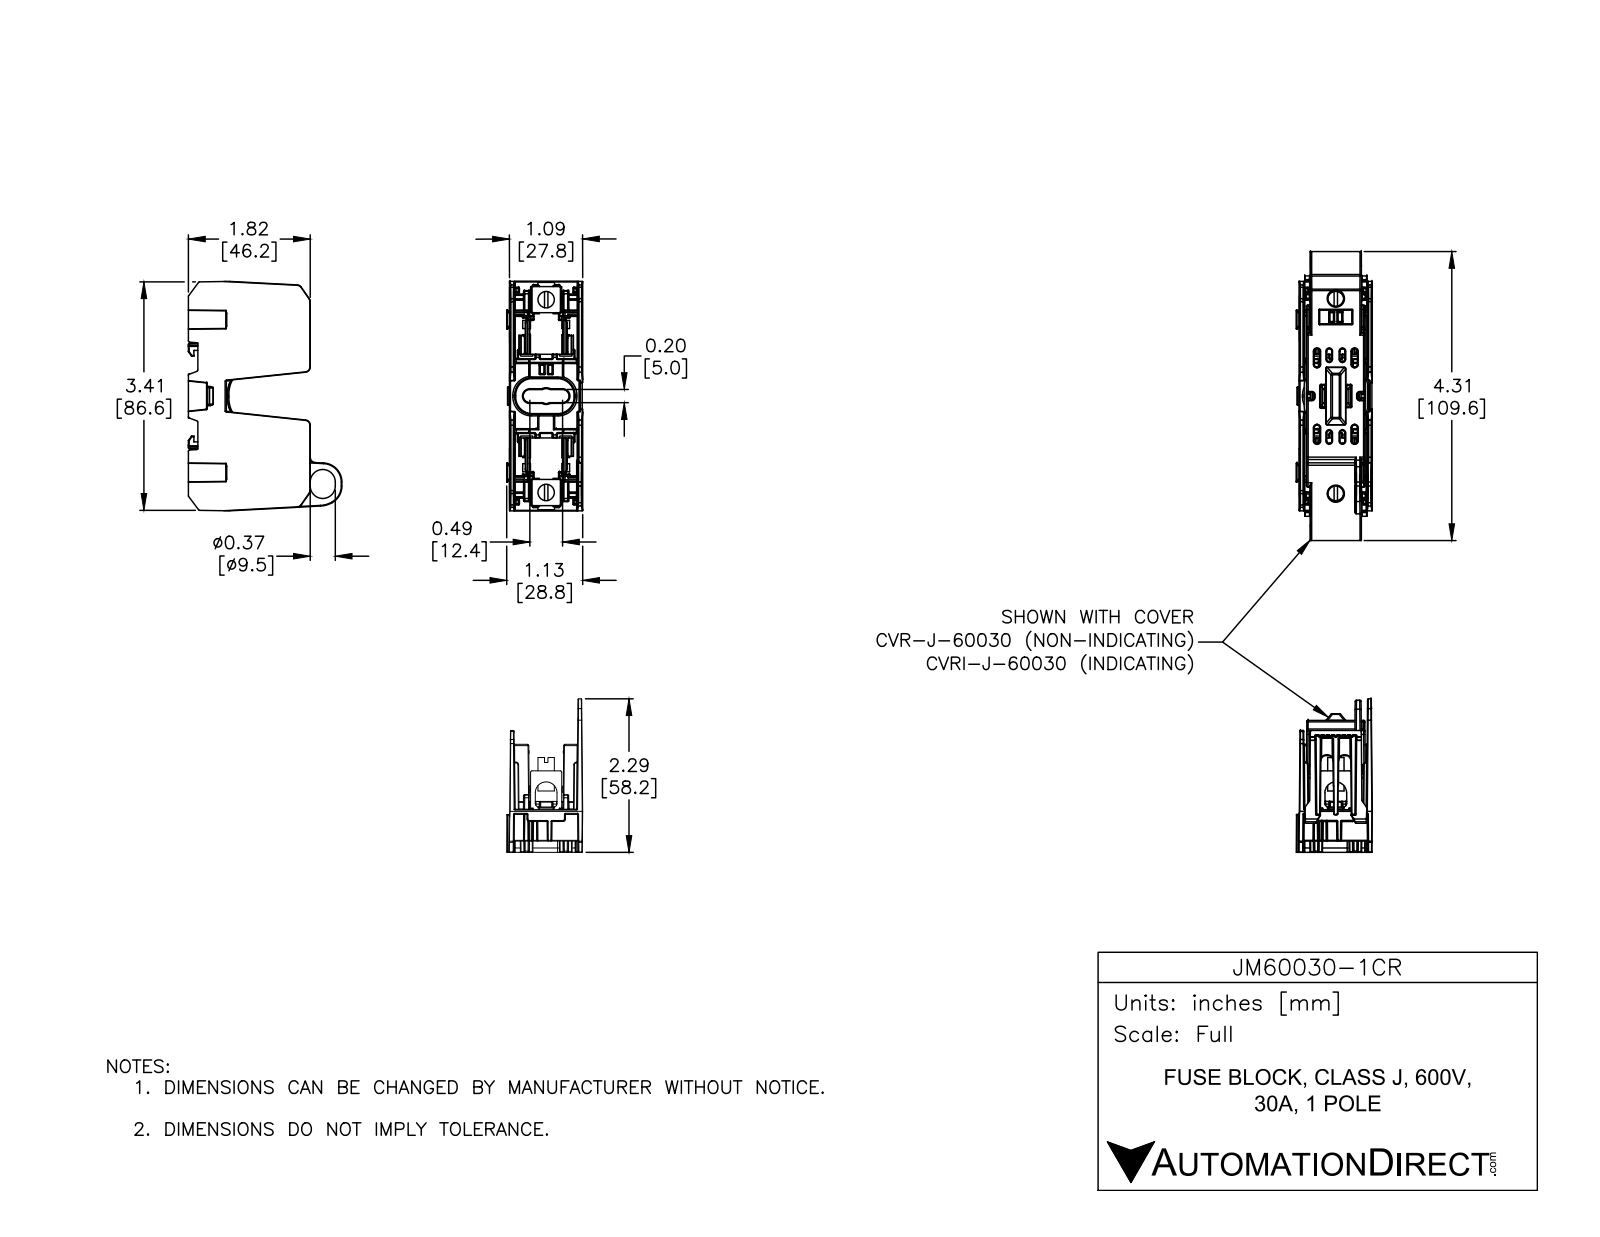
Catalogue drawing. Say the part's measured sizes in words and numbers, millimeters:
The part is named "JM60030-1CR". Its 3-D file was written by "SolidWorks 2016 (AUTOMOTIVE_DESIGN)". It is 13 solids with 3093 faces: 781 planar, 1329 cylindrical and 983 other. Overall it measures 87.2 by 58.2 by 28.8 millimeters. Its volume is 32 380 cubic millimeters and its surface area 33 300 square millimeters. Round holes: 2 of diameter 5.7, 2 of diameter 6.2. Round bosses or shafts: 2 of diameter 6.2. Partial cylindrical surfaces (rounded edges, fillets, slot ends): 416 of radius 0.3, 327 of radius 0.2, 57 of radius 0.5, 32 of radius 1, 24 of radius 0.1, 9 of radius 2, 8 of radius 0.5, 6 of radius 1.2. The main face-to-face distances are 25.7, 0.6, 25.8, 1.9, 27.7, 0.4, 1.7, 1.8, 2.2, 16.8. The hole center spacings are 15.1, 58, 42.9, 73.2.
